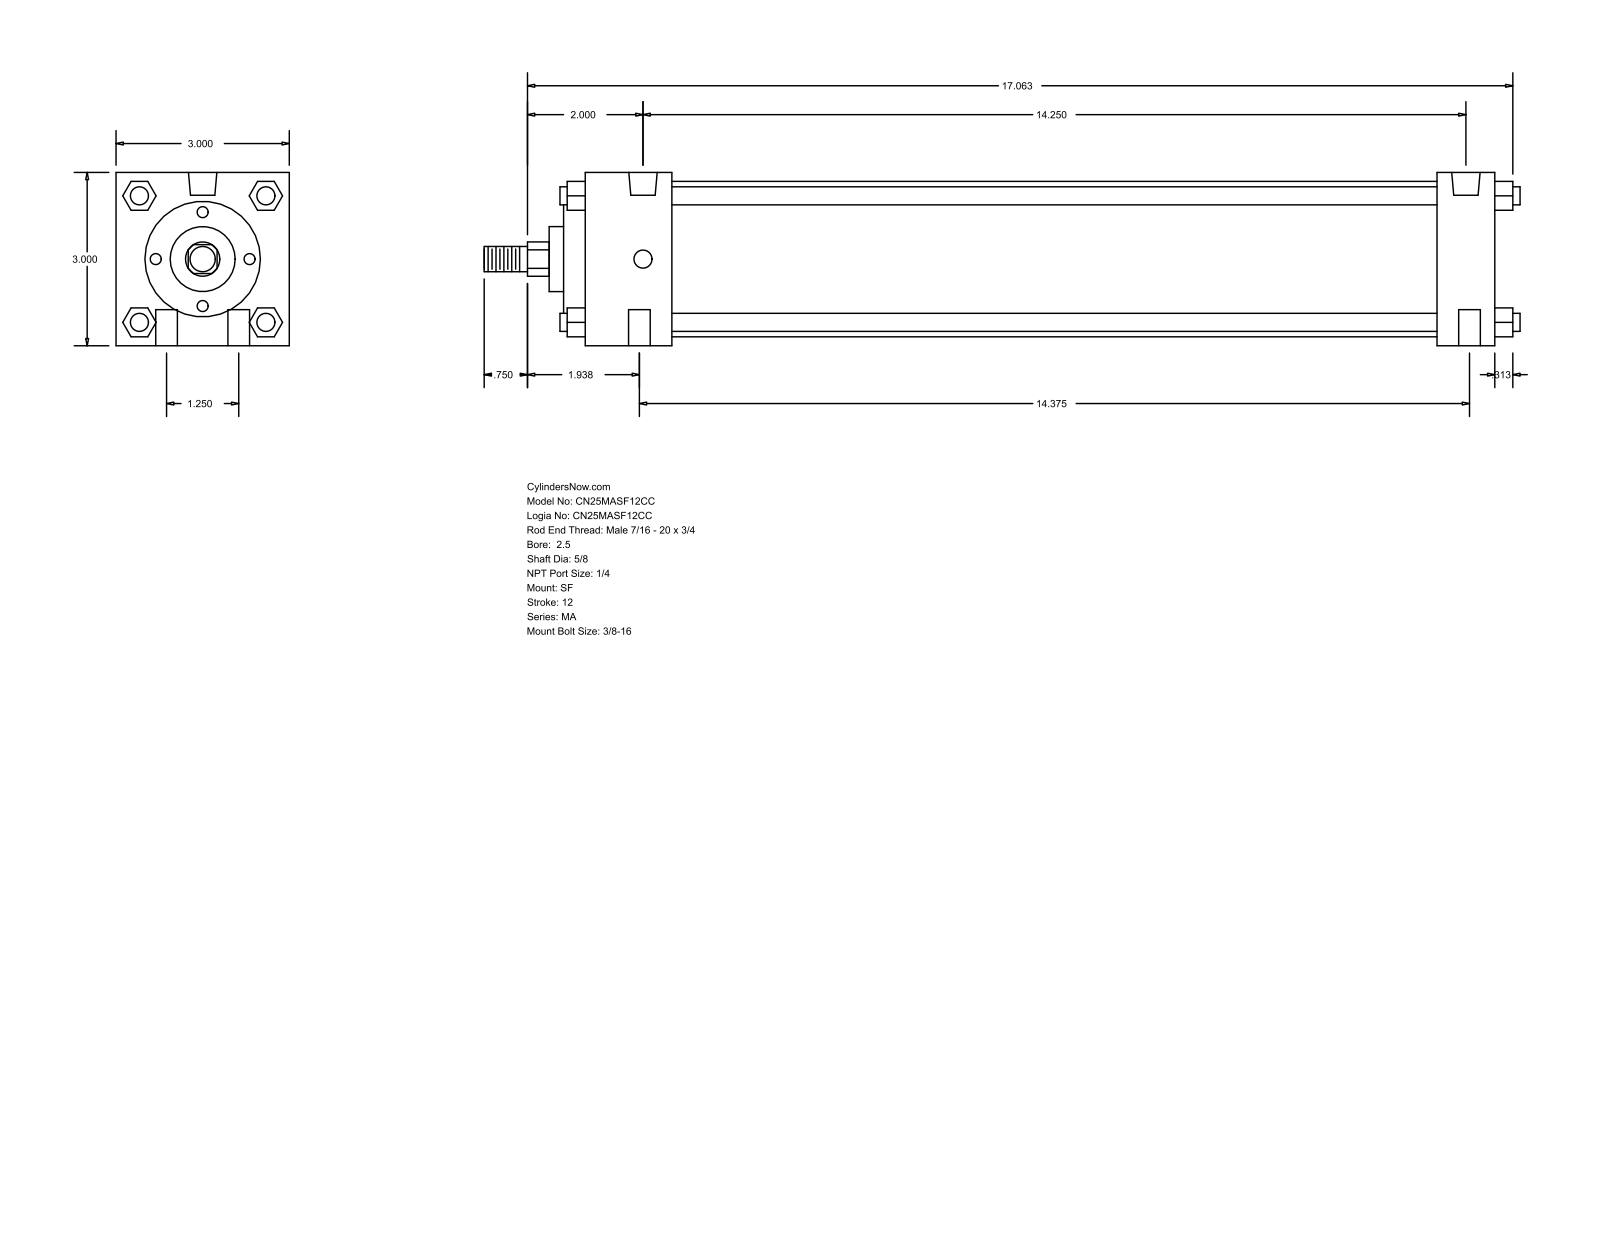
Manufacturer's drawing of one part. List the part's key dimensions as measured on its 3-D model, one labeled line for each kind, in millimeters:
Part name (STEP PRODUCT): MA_SF__0250_0.625
STEP written by: GSSL Pune (CONFIG_CONTROL_DESIGN)
Units: millimetres
Bodies: 0 solids, 126 faces (95 planar, 31 cylindrical, 0 other)
Overall size (bounding box): 455.61 × 76.2 × 76.2
Round holes (diameter × count): ⌀9.53 ×4, ⌀7.94 ×2, ⌀12.49 ×2
Round bosses / shafts (diameter × count): ⌀7.94 ×4, ⌀68.33 ×1, ⌀50.8 ×1, ⌀28.57 ×1, ⌀15.88 ×1, ⌀11.11 ×1
Partial cylindrical surfaces — rounded edges, fillets, slot ends (radius × count): R7.54 ×1
Main face-to-face distances: 76.2, 400.05, 25.4, 374.65, 38.1, 336.55, 361.95, 12.7, 9.52, 47.62
Hole centre spacings: 15.96, 363.89, 31.76, 361.95, 365.13, 366.51
